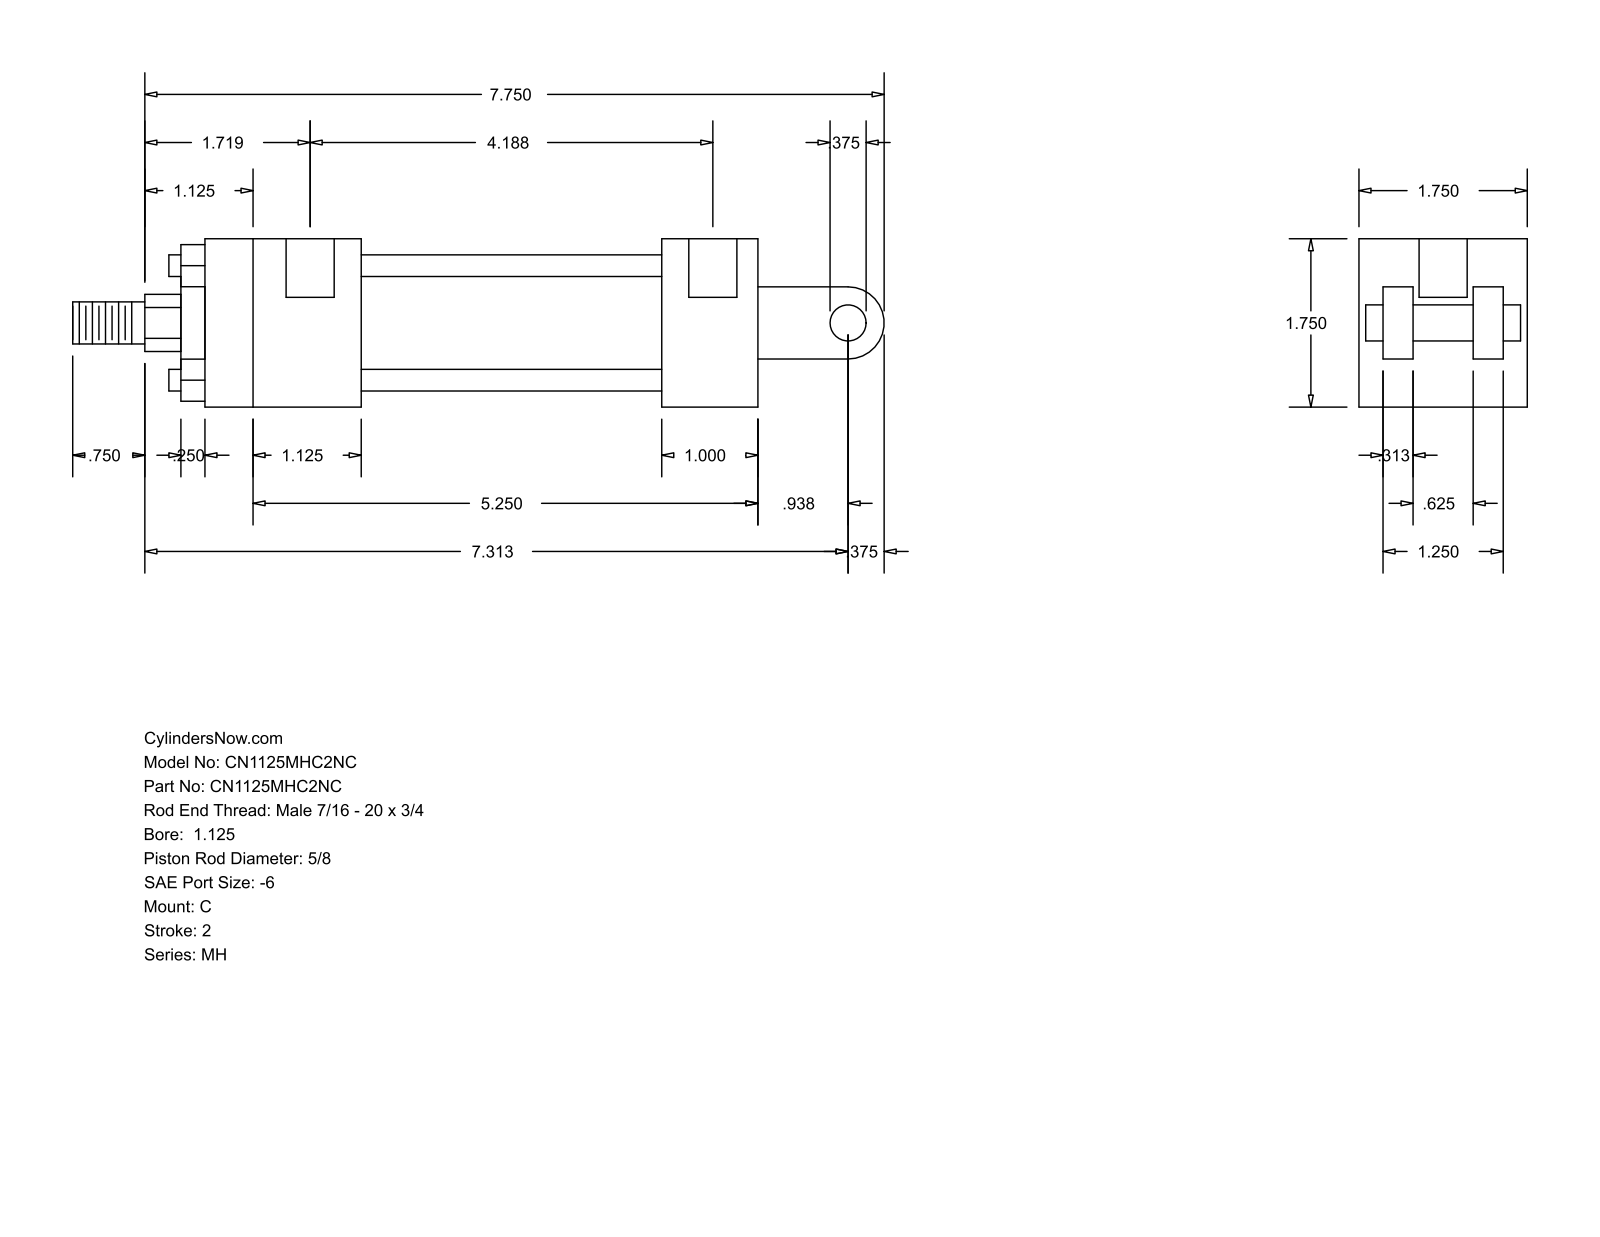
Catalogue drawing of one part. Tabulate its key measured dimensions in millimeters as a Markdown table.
| quantity | value |
| --- | --- |
| part name | MH_C__0112_0.625 |
| STEP written by | GSSL Pune (CONFIG_CONTROL_DESIGN) |
| units | millimeters |
| bodies | 0 solids, 99 faces (70 planar, 29 cylindrical, 0 other) |
| overall size | 214.31 × 44.45 × 44.45 |
| round holes (diameter × count) | 5.56 × 4, 12.7 × 2 |
| round bosses / shafts (diameter × count) | 5.71 × 4, 34.92 × 1, 28.57 × 1, 15.88 × 1, 11.11 × 1, 9.53 × 1 |
| partial cylindrical surfaces (radius × count) | 7.54 × 1, 9.53 × 1 |
| main face-to-face distances | 44.46, 6.35, 31.76, 14.29, 25.4, 30.17, 38.11, 7.94, 23.82, 41.27 |
| hole center spacings | 103.19, 3.17, 106.36 |
